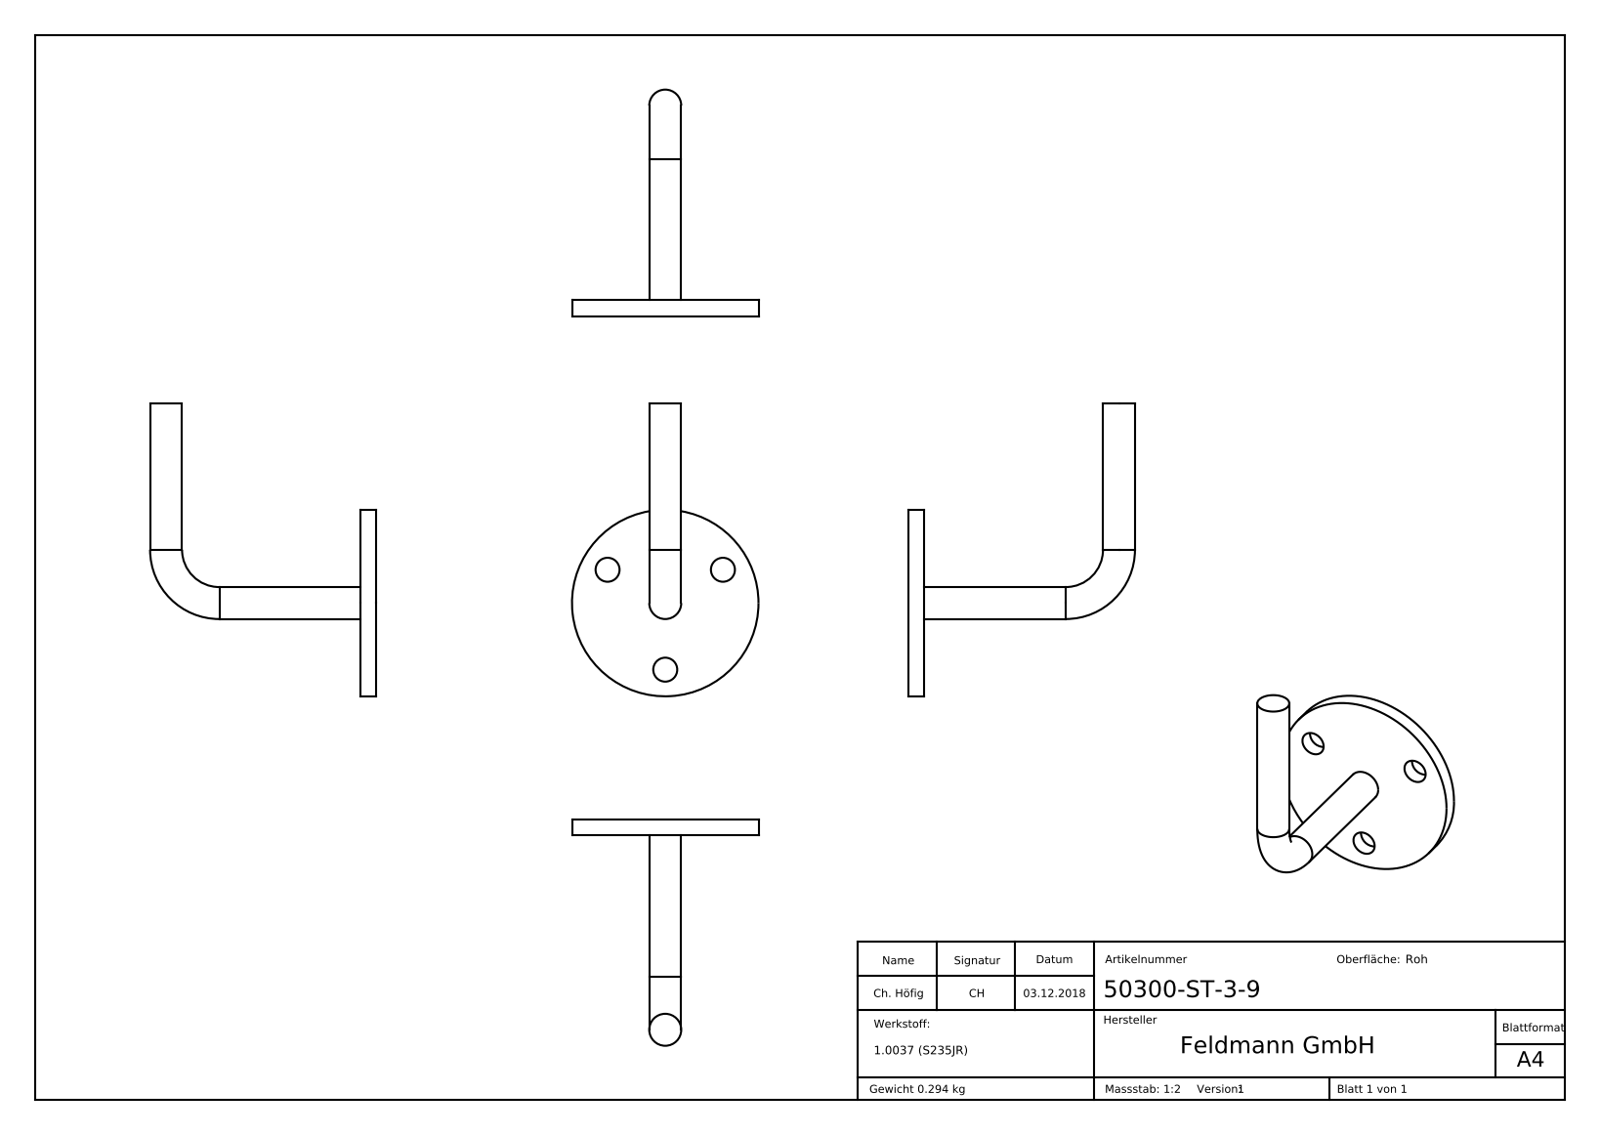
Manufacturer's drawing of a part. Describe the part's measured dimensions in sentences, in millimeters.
The part is named "50300-ST-3-9". Its 3-D file was written by "SolidWorks 2015 (CONFIG_CONTROL_DESIGN)". It is 1 solid with 270 faces: 121 planar, 12 cylindrical and 137 other. Overall it measures 110 by 85 by 70 millimeters. Its volume is 37 710 cubic millimeters and its surface area 14 452 square millimeters. Round holes: 3 of diameter 9. Round bosses or shafts: 2 of diameter 12, 1 of diameter 70. The main face-to-face distances are 6, 0.5, 5.5, 0.54, 0.67, 1.33, 0.79, 0.66, 0.72, 0.6. The hole center spacings are 43.3.
